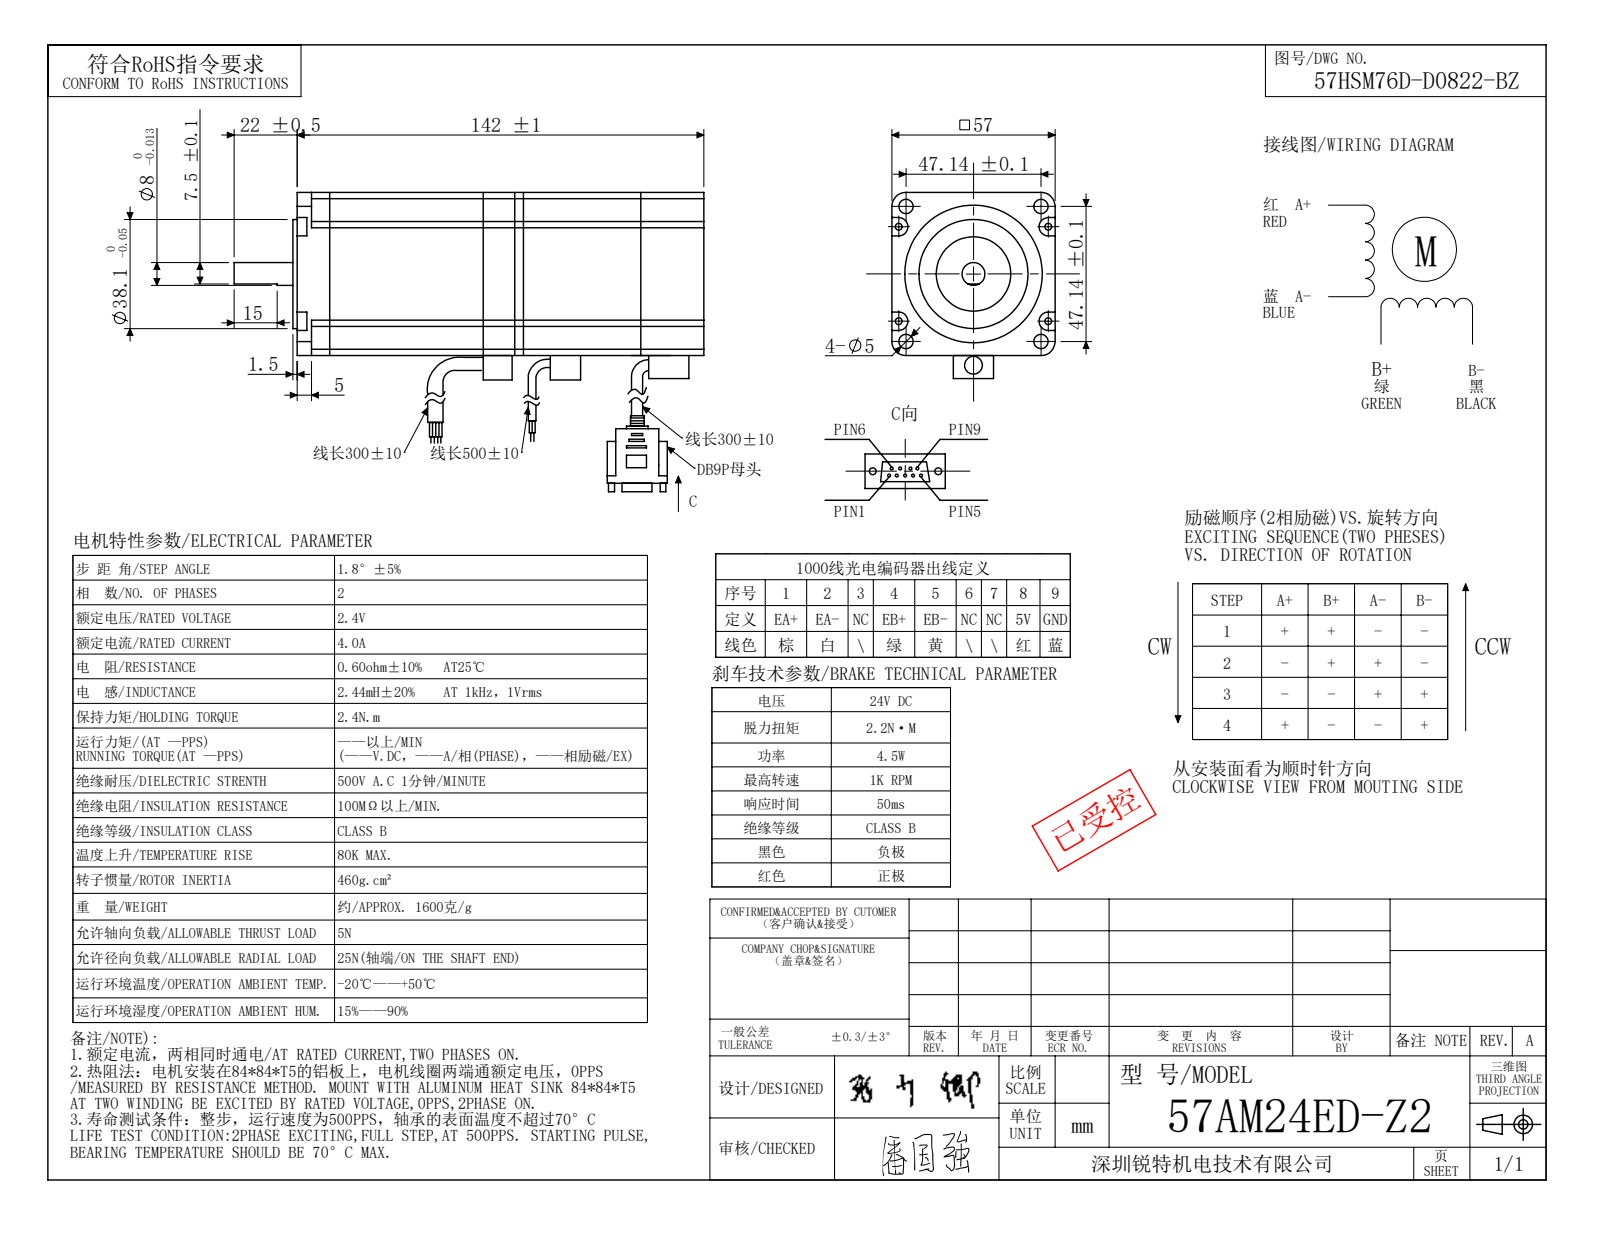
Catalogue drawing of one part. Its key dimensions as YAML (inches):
part_name: "57AM24ED-Z2(57HSM76D-D0822-BZ)"
step_written_by: "SolidWorks 2020 (CONFIG_CONTROL_DESIGN)"
units: inches
bodies: {solids: 1, faces: 78, planar: 32, cylindrical: 46, other: 0}
overall_size: [6.457, 2.244, 2.244]
volume: 25
surface_area: 61.99
round_holes:
  - {diameter: 0.094, count: 4}
  - {diameter: 0.197, count: 4}
  - {diameter: 1.024, count: 1}
  - {diameter: 1.89, count: 1}
round_bosses_or_shafts:
  - {diameter: 1.5, count: 1}
  - {diameter: 0.315, count: 1}
partial_cylinders:
  - {radius: 0.087, count: 8}
  - {radius: 0.126, count: 4}
  - {radius: 0.194, count: 4}
  - {radius: 0.315, count: 4}
face_to_face_distances: [2.244, 5.591, 5.561, 0.03, 5.65, 0.089, 0.059, 5.602, 0.041, 0.047]
hole_center_spacings: [0.296, 1.216, 1.312, 1.581, 1.856, 1.975, 2.513, 1.299]
